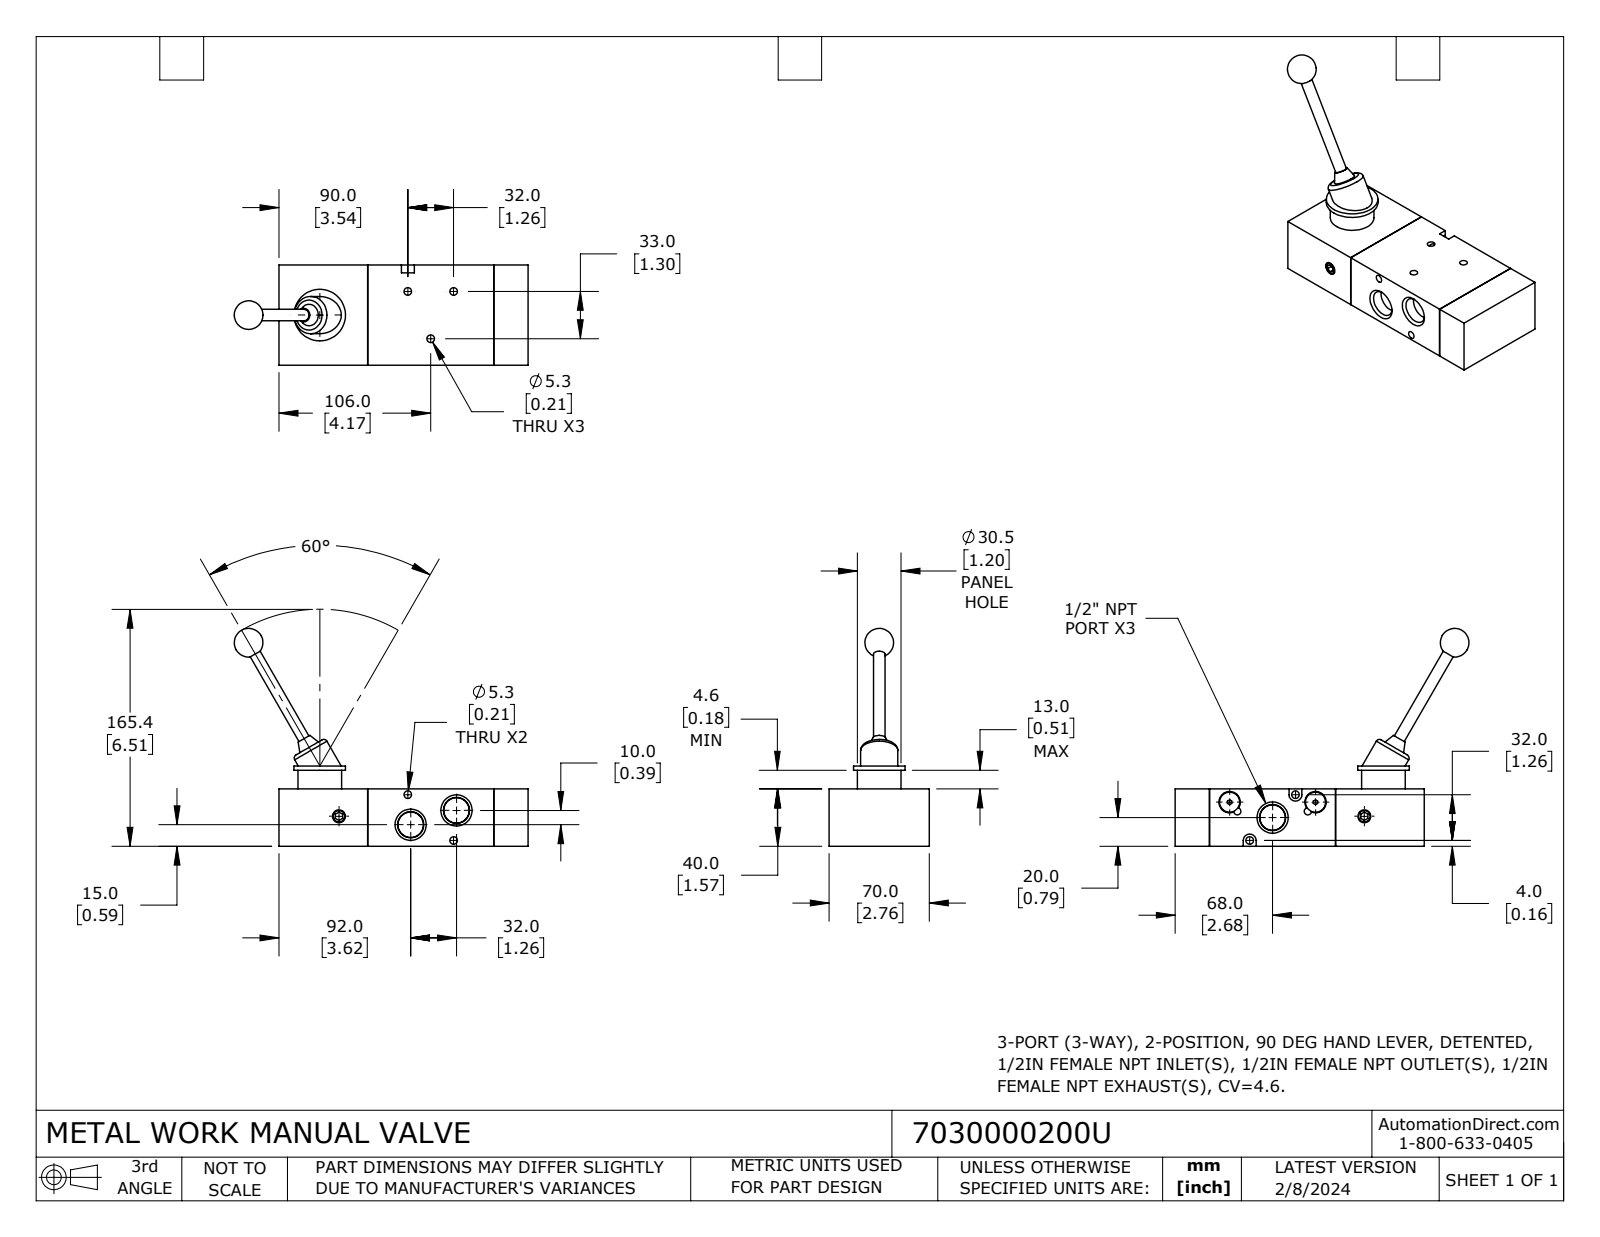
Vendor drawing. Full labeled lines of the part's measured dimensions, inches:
Part name (STEP PRODUCT): 7030000200U
STEP written by: SolidWorks 2023 (CONFIG_CONTROL_DESIGN)
Units: inches
Bodies: 3 solids, 136 faces (67 planar, 51 cylindrical, 18 other)
Overall size (bounding box): 8.079 × 5.988 × 2.756
Volume: 30.63 in³ · Surface area: 105.8 in²
Round holes (diameter × count): ⌀0.209 ×5, ⌀0.587 ×2, ⌀0.354 ×1
Round bosses / shafts (diameter × count): ⌀0.551 ×2, ⌀1.417 ×1, ⌀1.201 ×1, ⌀1.024 ×1, ⌀0.315 ×1, ⌀0.313 ×1
Partial cylindrical surfaces — rounded edges, fillets, slot ends (radius × count): R0.098 ×2, R0.177 ×2
Main face-to-face distances: 1.575, 2.756, 3.465, 0.945, 4.409, 6.85, 5.906, 2.441, 0.354, 2.402
Hole centre spacings: 1.444, 0.589, 1.188, 1.26, 1.397, 1.781, 1.823, 1.985
